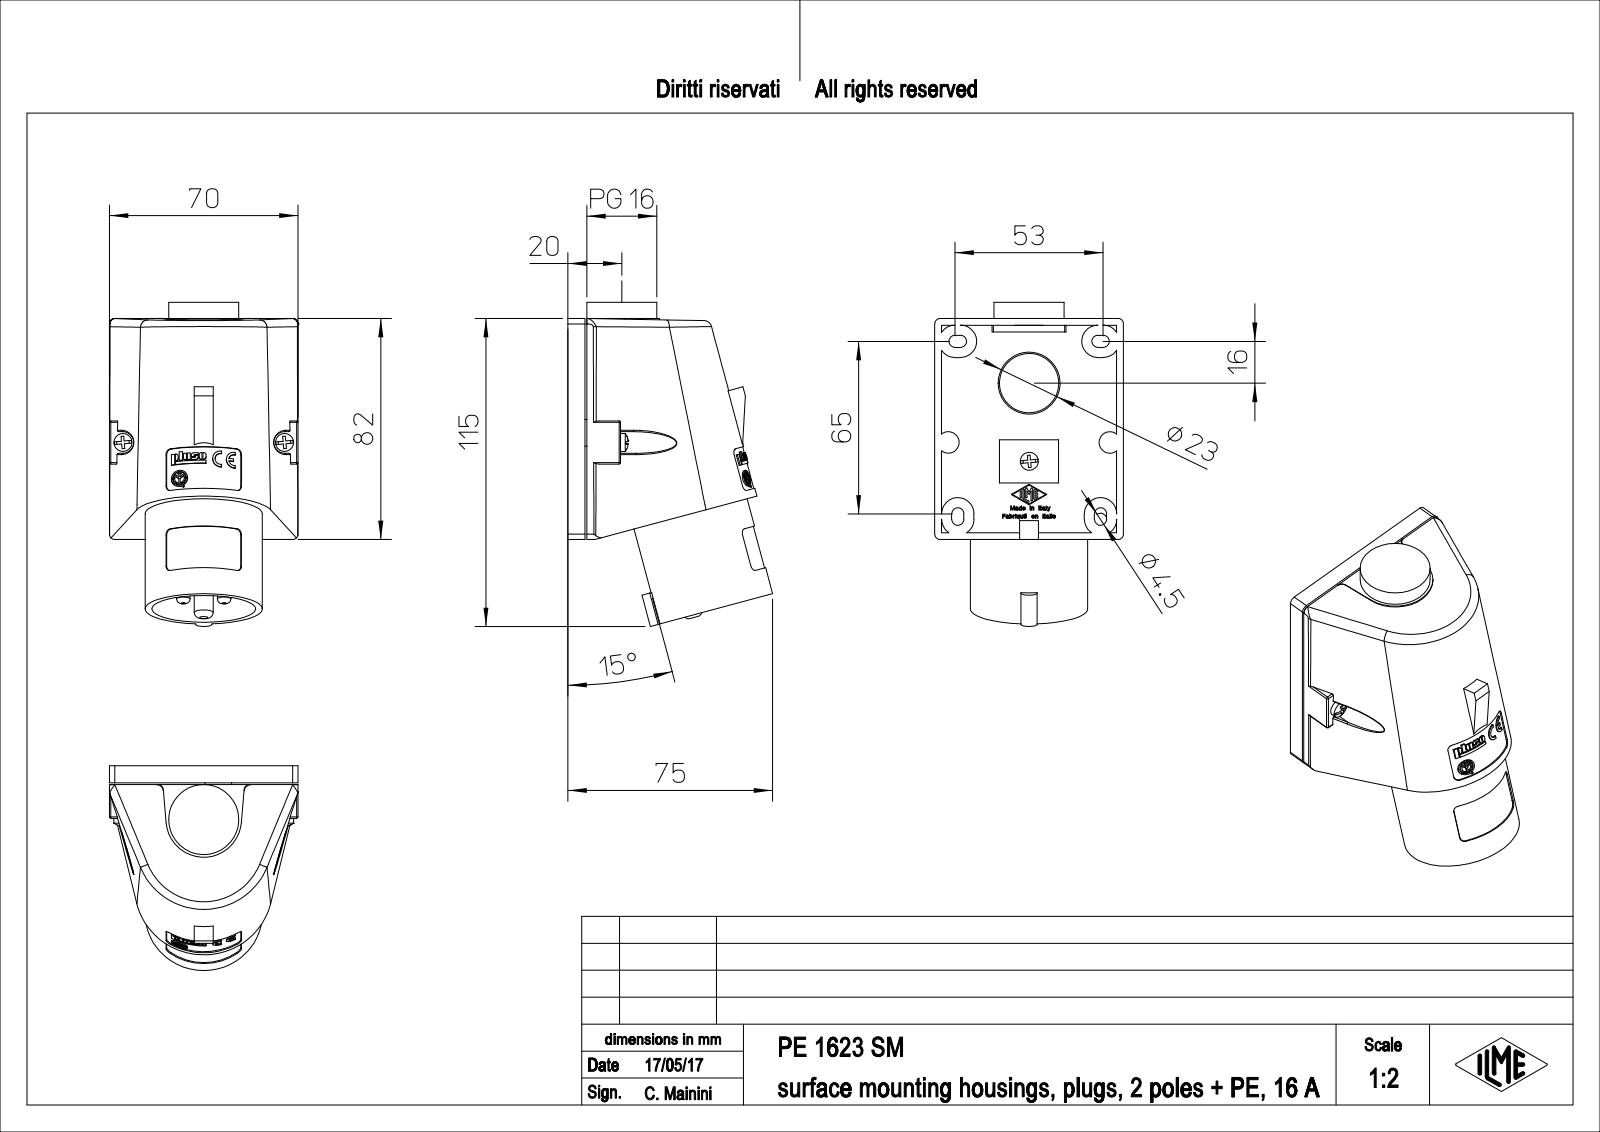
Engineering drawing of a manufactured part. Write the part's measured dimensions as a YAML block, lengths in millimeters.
part_name: "PE_1623_SM"
step_written_by: "PTC Creo Elements/Direct Modeling 19.0E 27-Jun-2016 (C) Parametric Technology GmbH (AUTOMOTIVE_DESIGN)"
units: millimeters
bodies: {solids: 1, faces: 1394, planar: 1127, cylindrical: 167, other: 100}
overall_size: [120.27, 75.98, 70]
volume: 248744
surface_area: 55760
round_holes:
  - {diameter: 3.2, count: 2}
  - {diameter: 4.5, count: 2}
  - {diameter: 4.2, count: 1}
  - {diameter: 5.04, count: 1}
  - {diameter: 21.3, count: 1}
  - {diameter: 23, count: 1}
  - {diameter: 24, count: 1}
  - {diameter: 38.5, count: 1}
round_bosses_or_shafts:
  - {diameter: 6.7, count: 5}
  - {diameter: 5, count: 2}
  - {diameter: 43.5, count: 1}
  - {diameter: 37, count: 1}
  - {diameter: 26, count: 1}
  - {diameter: 7, count: 1}
  - {diameter: 6, count: 1}
partial_cylinders:
  - {radius: 2, count: 16}
  - {radius: 0.25, count: 15}
  - {radius: 0.5, count: 9}
  - {radius: 0.85, count: 9}
  - {radius: 2.25, count: 8}
  - {radius: 4, count: 8}
  - {radius: 6, count: 8}
  - {radius: 0.12, count: 3}
face_to_face_distances: [0.65, 6, 5.35, 7, 1, 6.35, 70, 2.5, 3, 82]
hole_center_spacings: [30.81, 37.2, 29, 60]
